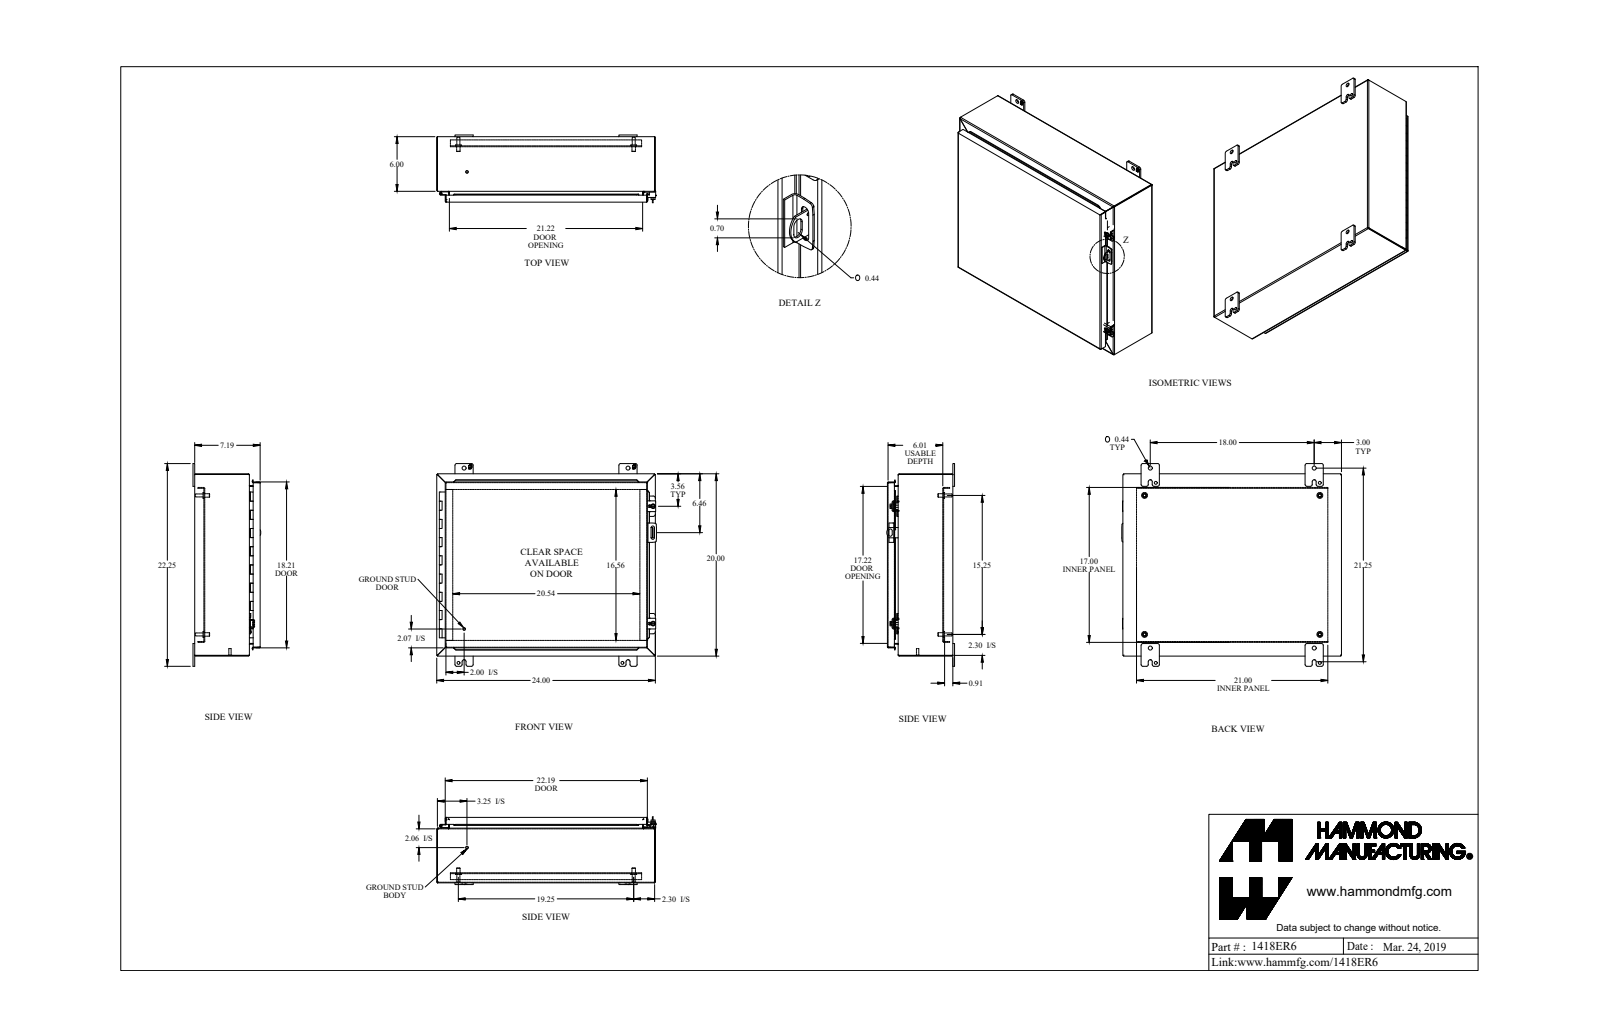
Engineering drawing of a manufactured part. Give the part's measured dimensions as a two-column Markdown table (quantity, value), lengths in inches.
| quantity | value |
| --- | --- |
| part name | 1418ER6 |
| STEP written by | SolidWorks 2019 (AUTOMOTIVE_DESIGN) |
| units | inches |
| bodies | 38 solids, 978 faces (671 planar, 255 cylindrical, 52 other) |
| overall size | 24.125 × 22.25 × 7.437 |
| volume | 176.1 in³ |
| surface area | 4 537 in² |
| round holes (diameter × count) | 0.313 × 4, 0.437 × 4, 0.5 × 4, 0.213 × 2, 0.265 × 2, 0.307 × 2, 0.375 × 2, 0.445 × 2, 0.125 × 1, 0.187 × 1 |
| round bosses / shafts (diameter × count) | 0.65 × 4, 0.375 × 4, 0.33 × 4, 1 × 2, 0.5 × 2, 0.39 × 2, 0.281 × 2, 0.25 × 2 |
| partial cylindrical surfaces (radius × count) | 0.188 × 26, 0.036 × 20, 0.108 × 20, 0.048 × 13, 0.143 × 13, 0.045 × 8, 0.218 × 8, 0.25 × 8 |
| main face-to-face distances | 0.072, 7.113, 7.041, 7.185, 0.937, 0.095, 1.009, 6.081, 6.009, 1.032 |
| hole center spacings | 18, 19.25, 24.559, 26.722, 1.736, 19.75, 21.408, 25.587 |
